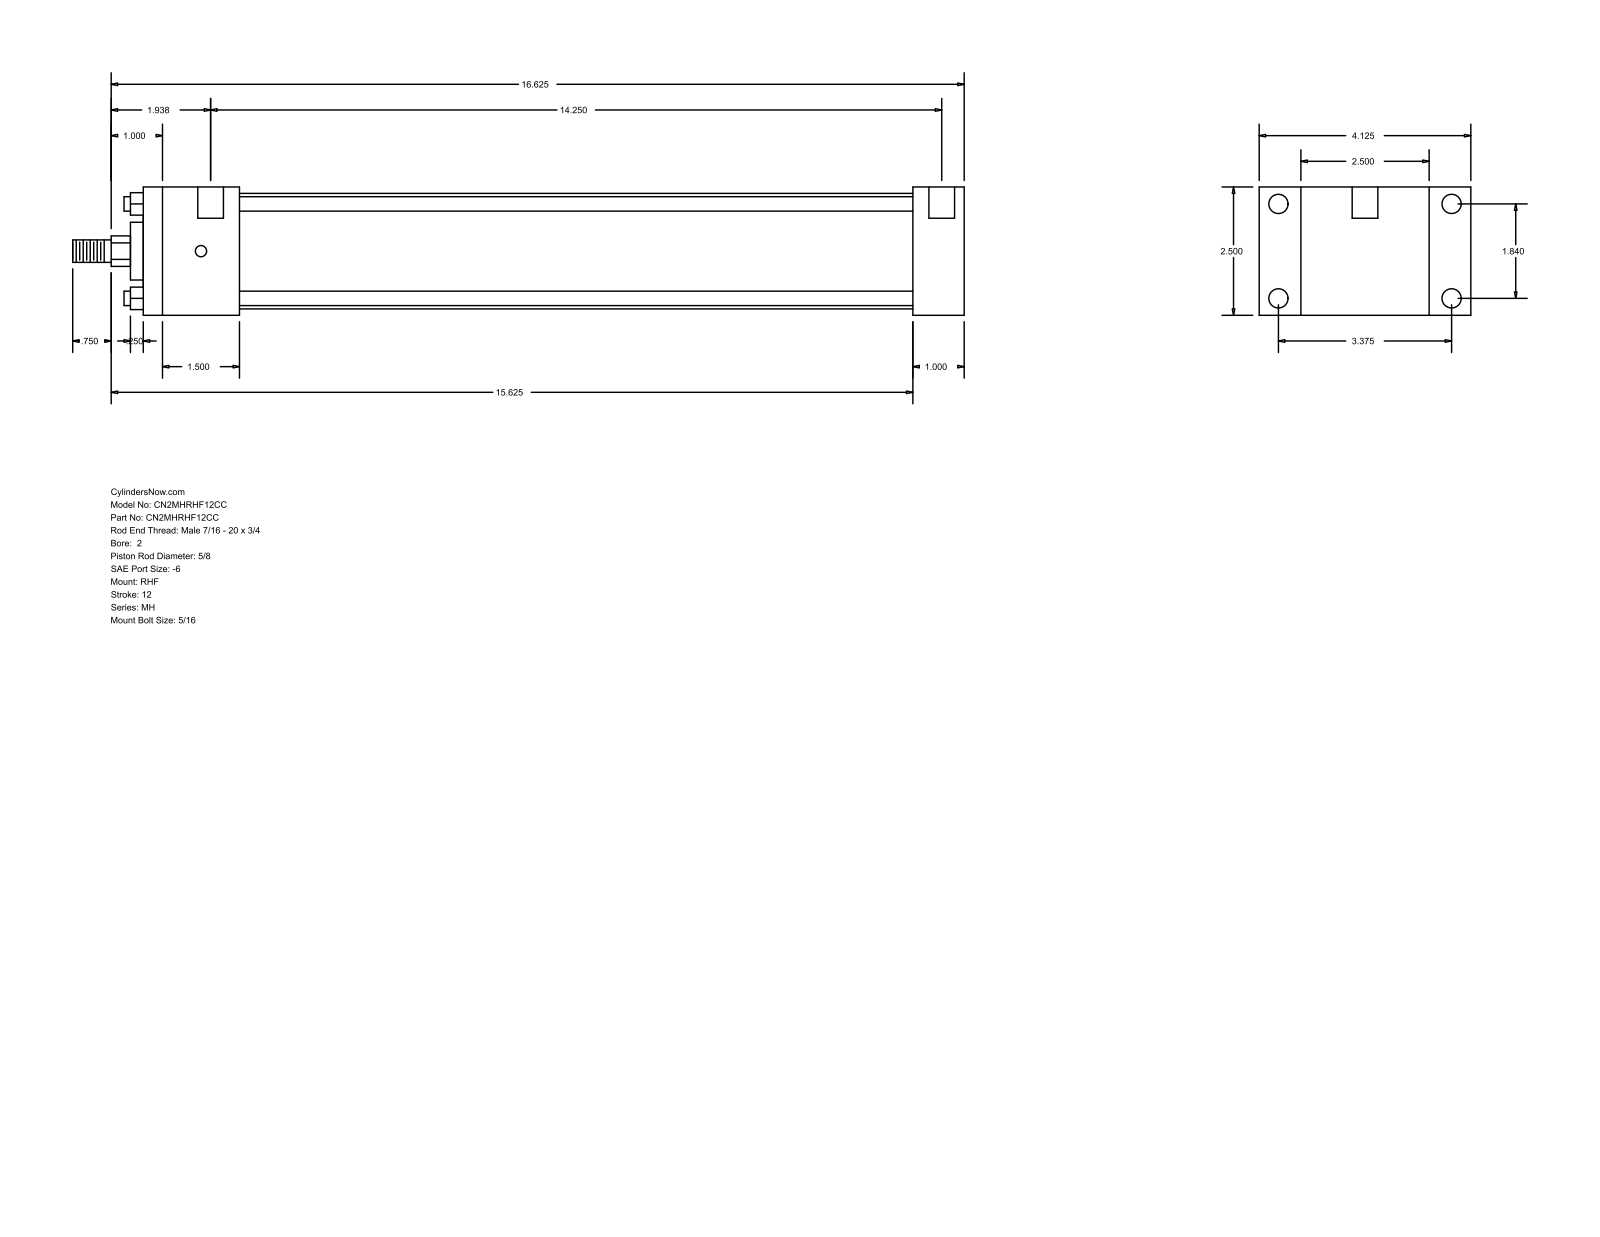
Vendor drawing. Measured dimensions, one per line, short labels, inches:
name: MH_RHF__0200_0.625
written by: GSSL Pune (CONFIG_CONTROL_DESIGN)
unit: in
bodies: 0 solids, 88 faces (60 planar, 28 cylindrical, 0 other)
size: 17.375 × 4.125 × 2.5
holes: 4× ⌀0.219, 4× ⌀0.375, 2× ⌀0.5
bosses: 4× ⌀0.281, 1× ⌀2.25, 1× ⌀1.125, 1× ⌀0.625, 1× ⌀0.437
rounds: 1× R0.297
face distances: 2.5, 1, 0.813, 3.313, 15, 16, 4.125, 1.875, 13.125, 14.125
hole spacings: 1.84, 3.375, 3.844, 14.563, 0.125, 0.187, 14.25, 14.375
